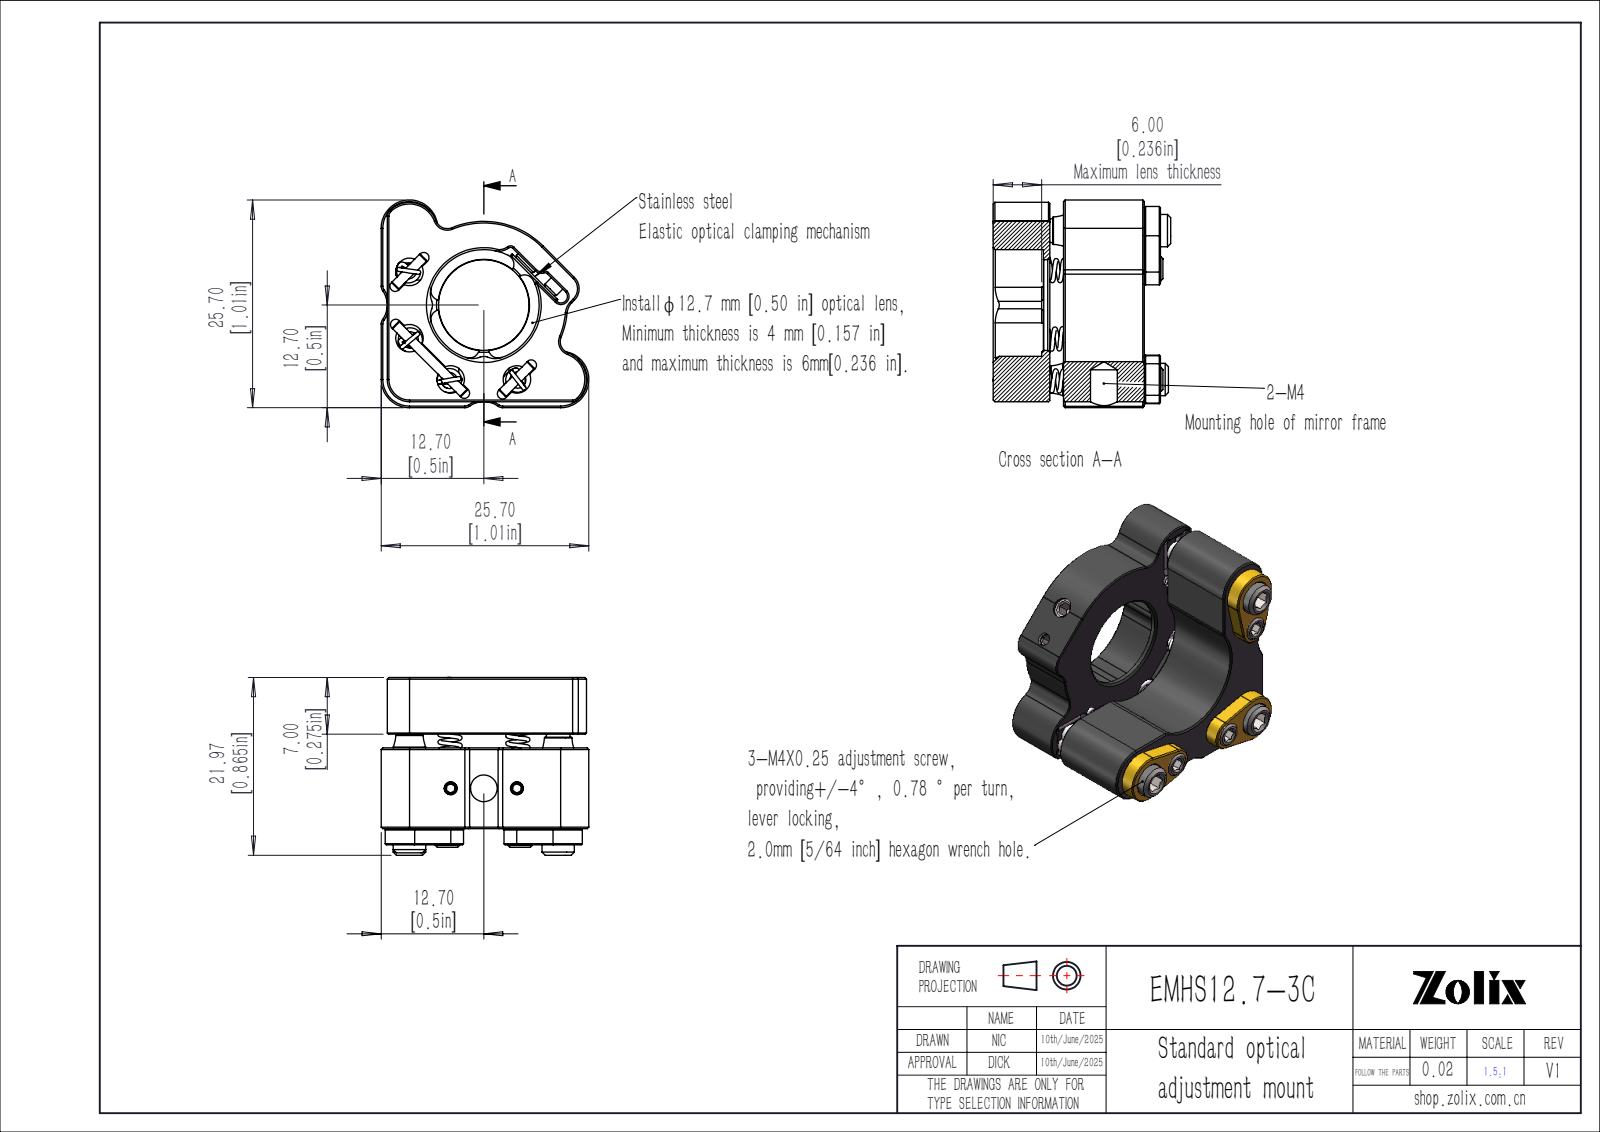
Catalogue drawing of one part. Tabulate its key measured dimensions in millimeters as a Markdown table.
| quantity | value |
| --- | --- |
| part name | EMHS12.7-3C |
| STEP written by | SolidWorks 2020 (CONFIG_CONTROL_DESIGN) |
| units | millimeters |
| bodies | 0 solids, 624 faces (220 planar, 163 cylindrical, 241 other) |
| overall size | 25.7 × 25.7 × 21.03 |
| round holes (diameter × count) | 1.6 × 5, 3.4 × 4, 3.5 × 4, 3.3 × 2, 2.5 × 1, 11.2 × 1 |
| round bosses / shafts (diameter × count) | 1.2 × 7, 3 × 4, 4 × 3, 2 × 1 |
| partial cylindrical surfaces (radius × count) | 0.65 × 14, 1 × 9, 1.25 × 8, 2 × 6, 3.5 × 5, 1.5 × 4, 2.5 × 4, 0.2 × 3 |
| main face-to-face distances | 7, 0.75, 18.7, 11.7, 1.7, 8.7, 10, 6.25, 2, 0.8 |
| hole center spacings | 4.1, 8.2, 10.07, 14.24, 4.5, 7.21, 18.81 |
